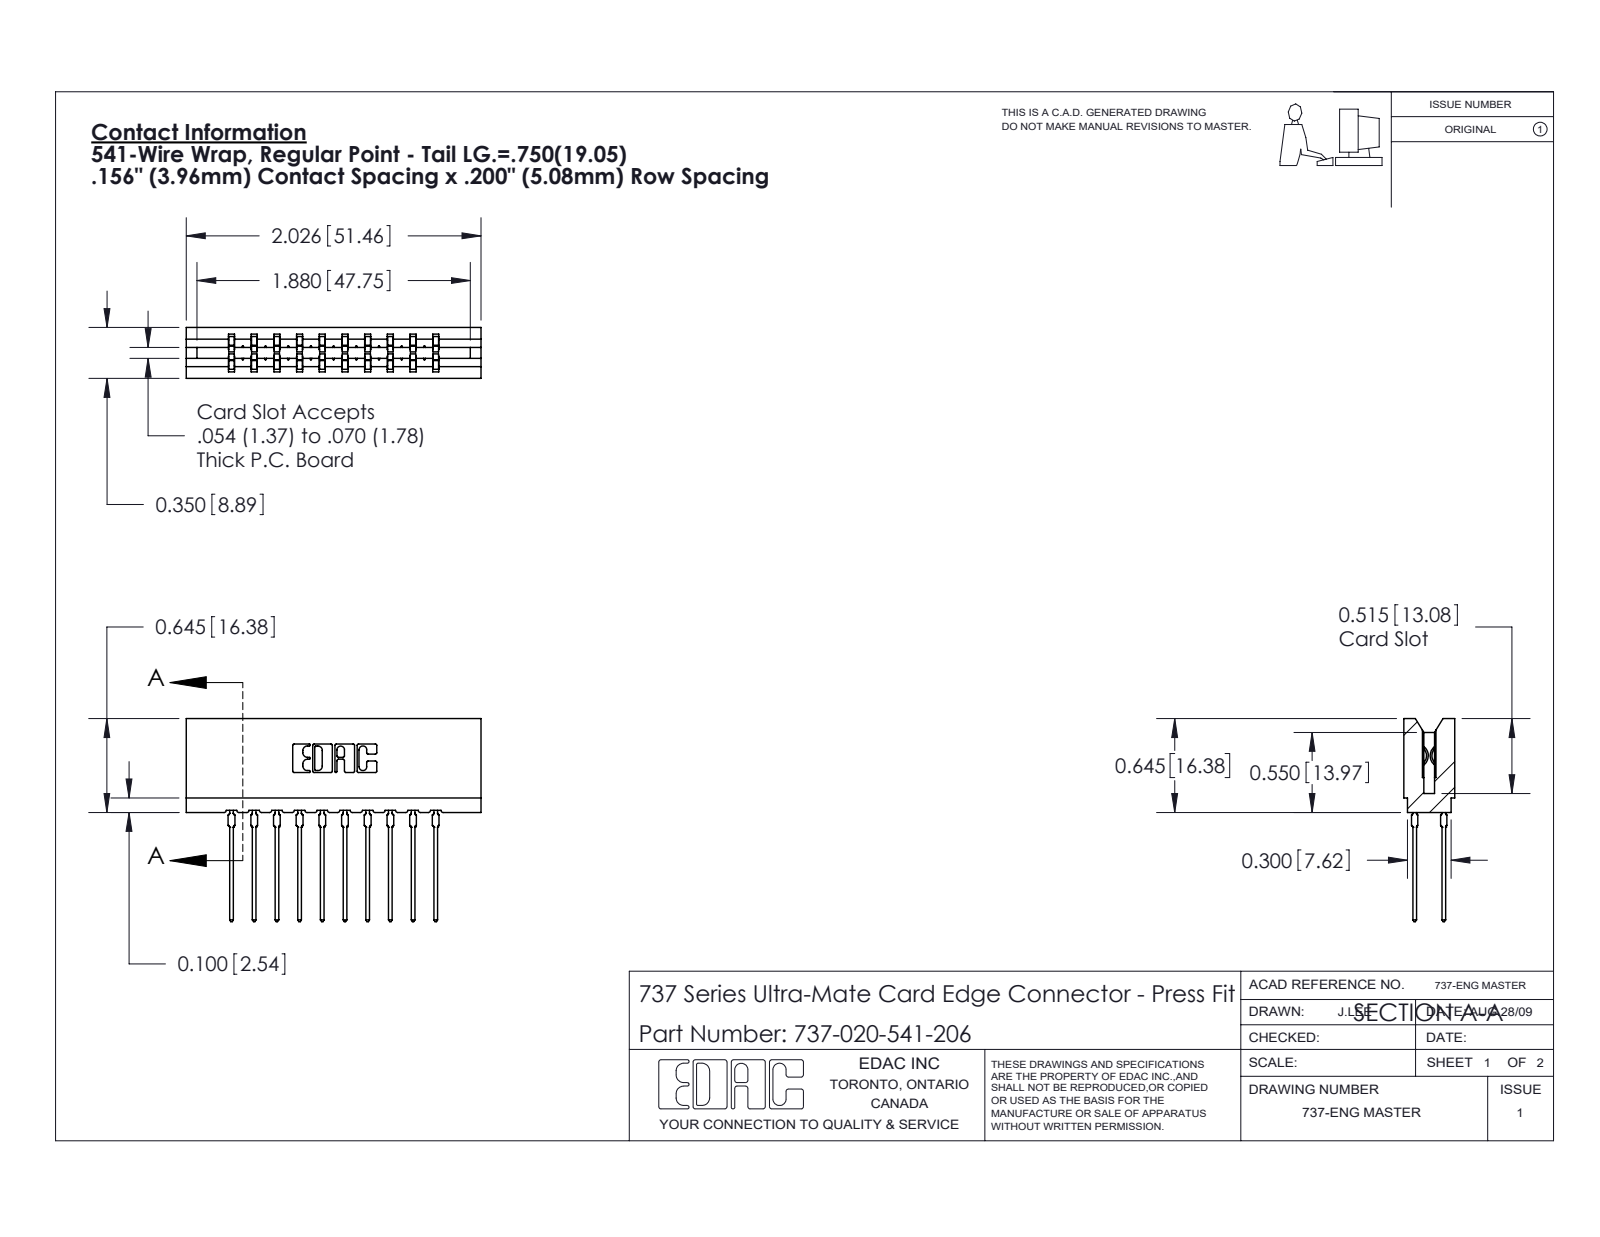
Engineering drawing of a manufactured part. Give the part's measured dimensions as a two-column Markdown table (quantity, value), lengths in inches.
| quantity | value |
| --- | --- |
| part name | 737 Part_Insulator Option - 06; 737-020-541-206; 745-292-001_541 |
| STEP written by | SolidWorks 2020 (CONFIG_CONTROL_DESIGN) |
| units | inches |
| bodies | 21 solids, 1895 faces (985 planar, 390 cylindrical, 520 other) |
| overall size | 2.026 × 1.396 × 0.35 |
| volume | 0.328 in³ |
| surface area | 11.7 in² |
| partial cylindrical surfaces (radius × count) | 0.021 × 40, 0.01 × 22, 0.015 × 20, 0.005 × 8, 0.011 × 8, 0.007 × 6, 0.031 × 6, 0.026 × 3 |
| main face-to-face distances | 0.156, 0.138, 0.212, 0.35, 0.624, 0.312, 0.354, 0.78, 0.468, 0.063 |
